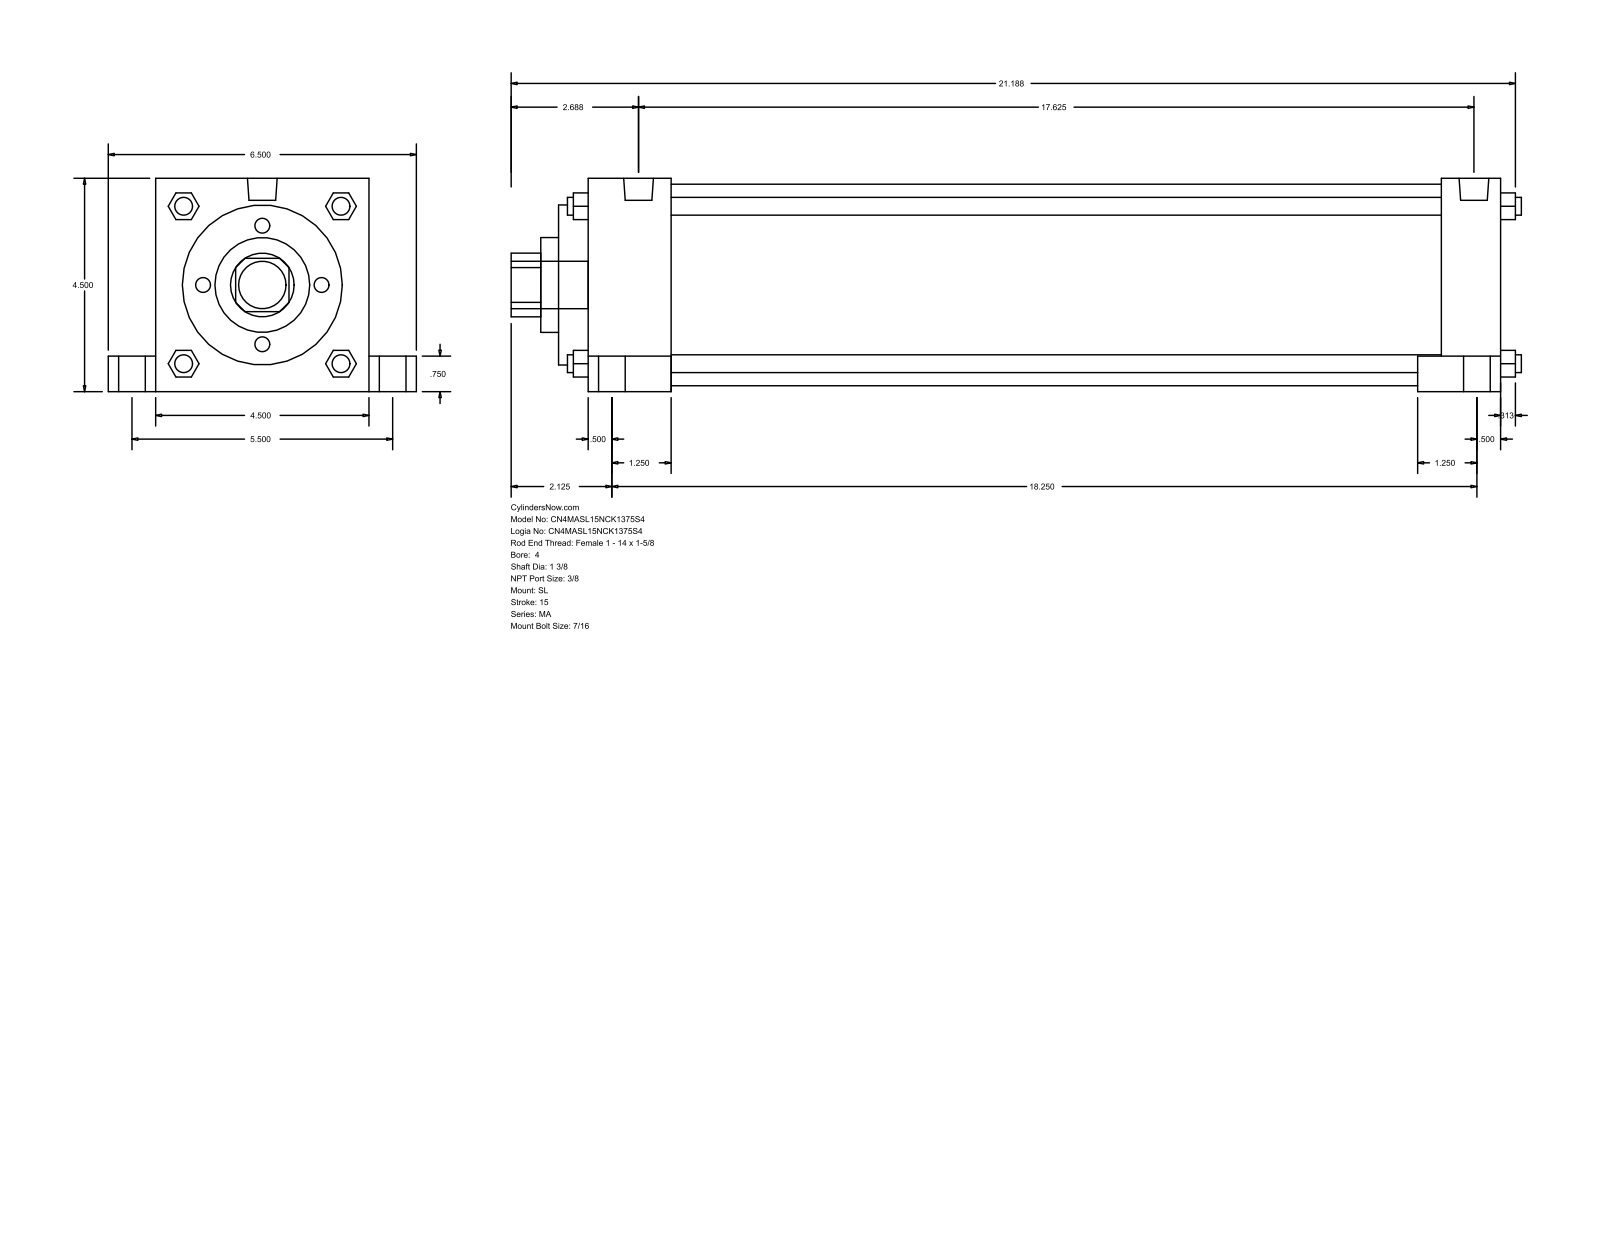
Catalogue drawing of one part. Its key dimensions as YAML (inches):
part_name: "MA_SL__0400_1.375"
step_written_by: "GSSL Pune (CONFIG_CONTROL_DESIGN)"
units: inches
bodies: {solids: 0, faces: 150, planar: 113, cylindrical: 37, other: 0}
overall_size: [21.313, 6.5, 4.5]
round_holes:
  - {diameter: 1.375, count: 1}
  - {diameter: 2, count: 1}
  - {diameter: 3.375, count: 1}
  - {diameter: 4.25, count: 1}
round_bosses_or_shafts:
  - {diameter: 0.813, count: 4}
  - {diameter: 0.563, count: 4}
  - {diameter: 0.437, count: 4}
  - {diameter: 0.375, count: 4}
  - {diameter: 0.627, count: 2}
  - {diameter: 1, count: 1}
partial_cylinders:
  - {radius: 0.672, count: 1}
face_to_face_distances: [4.5, 19.25, 0.625, 19.875, 2.375, 1.75, 17.5, 18.625, 18, 16.25]
